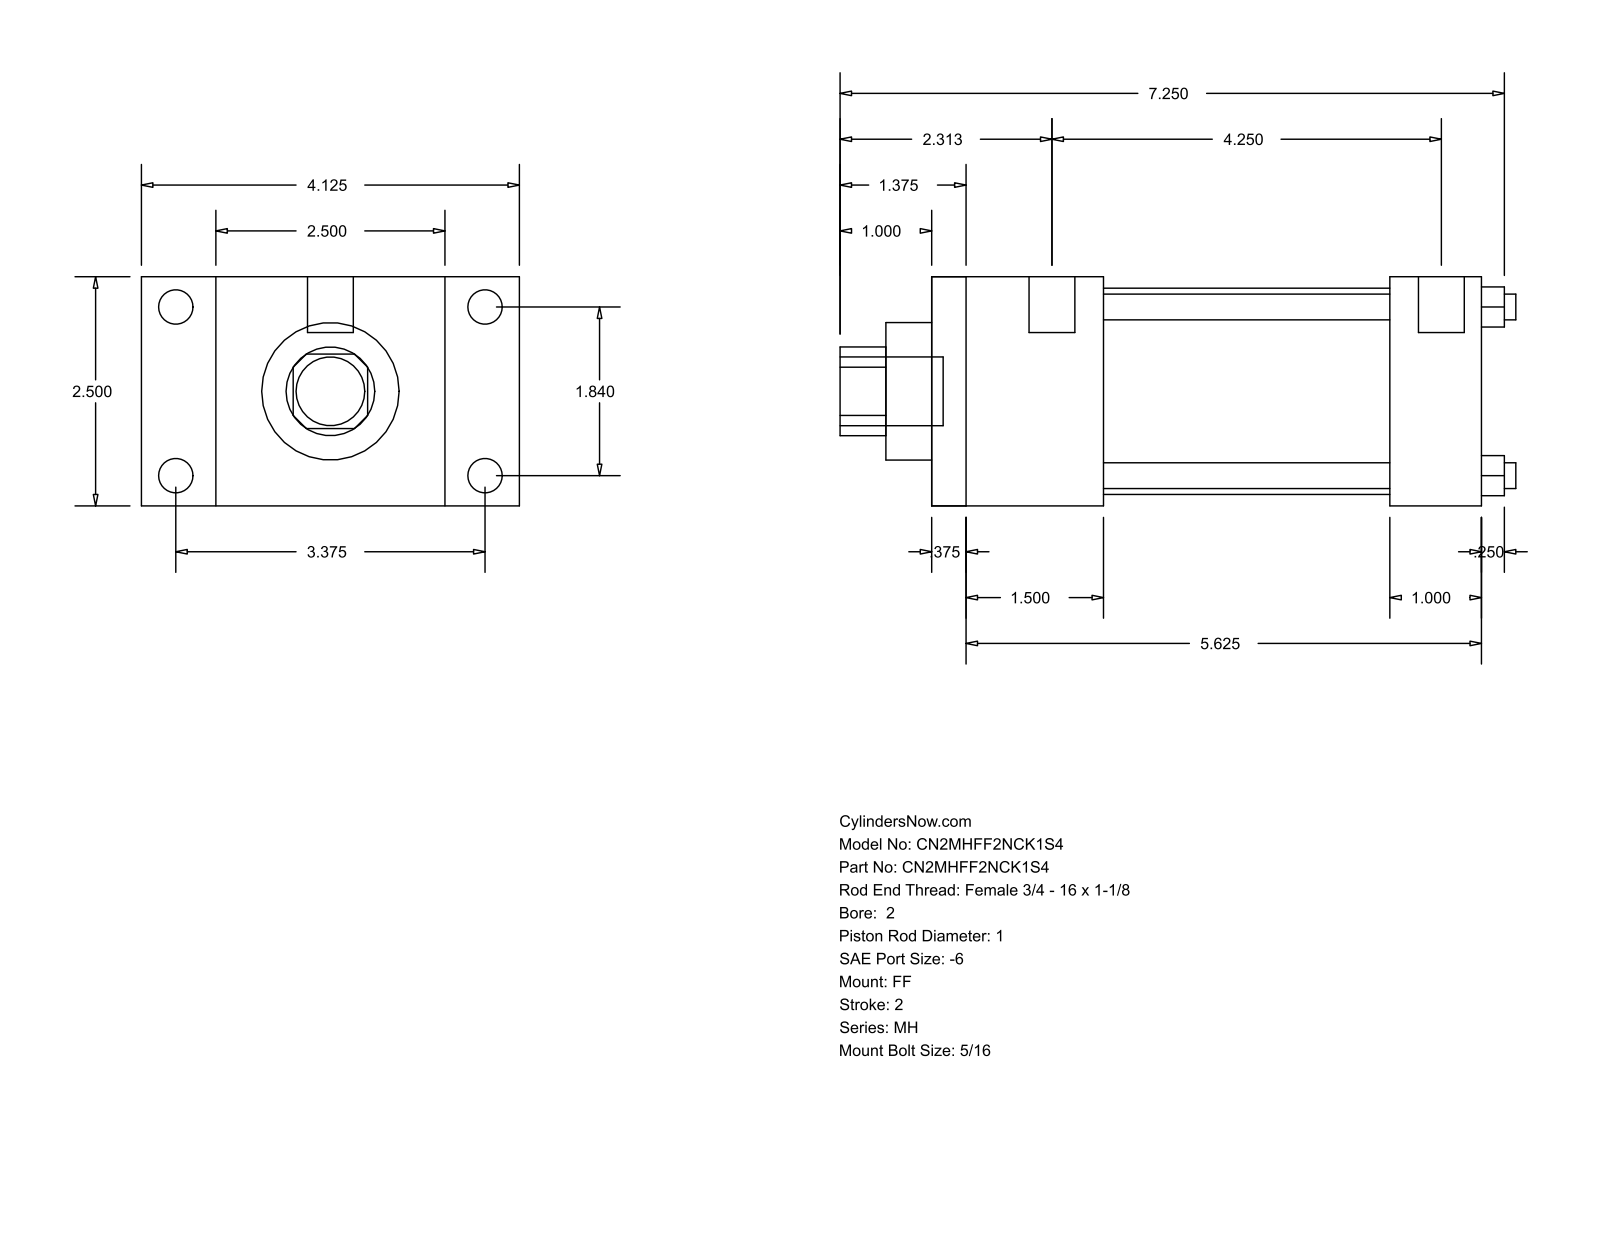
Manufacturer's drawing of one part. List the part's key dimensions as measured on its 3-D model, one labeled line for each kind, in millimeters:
Part name (STEP PRODUCT): MH_FF__0200_1
STEP written by: GSSL Pune (CONFIG_CONTROL_DESIGN)
Units: millimetres
Bodies: 0 solids, 92 faces (64 planar, 28 cylindrical, 0 other)
Overall size (bounding box): 187.32 × 104.78 × 63.5
Round holes (diameter × count): ⌀7.14 ×4, ⌀25.4 ×1, ⌀38.1 ×1, ⌀57.15 ×1
Round bosses / shafts (diameter × count): ⌀9.53 ×4, ⌀5.56 ×4, ⌀12.7 ×2, ⌀19.05 ×1
Partial cylindrical surfaces — rounded edges, fillets, slot ends (radius × count): R12.29 ×1
Main face-to-face distances: 63.5, 152.4, 9.52, 142.88, 20.64, 25.4, 47.63, 127, 38.11, 117.48
Hole centre spacings: 33.05, 46.74, 66.1
